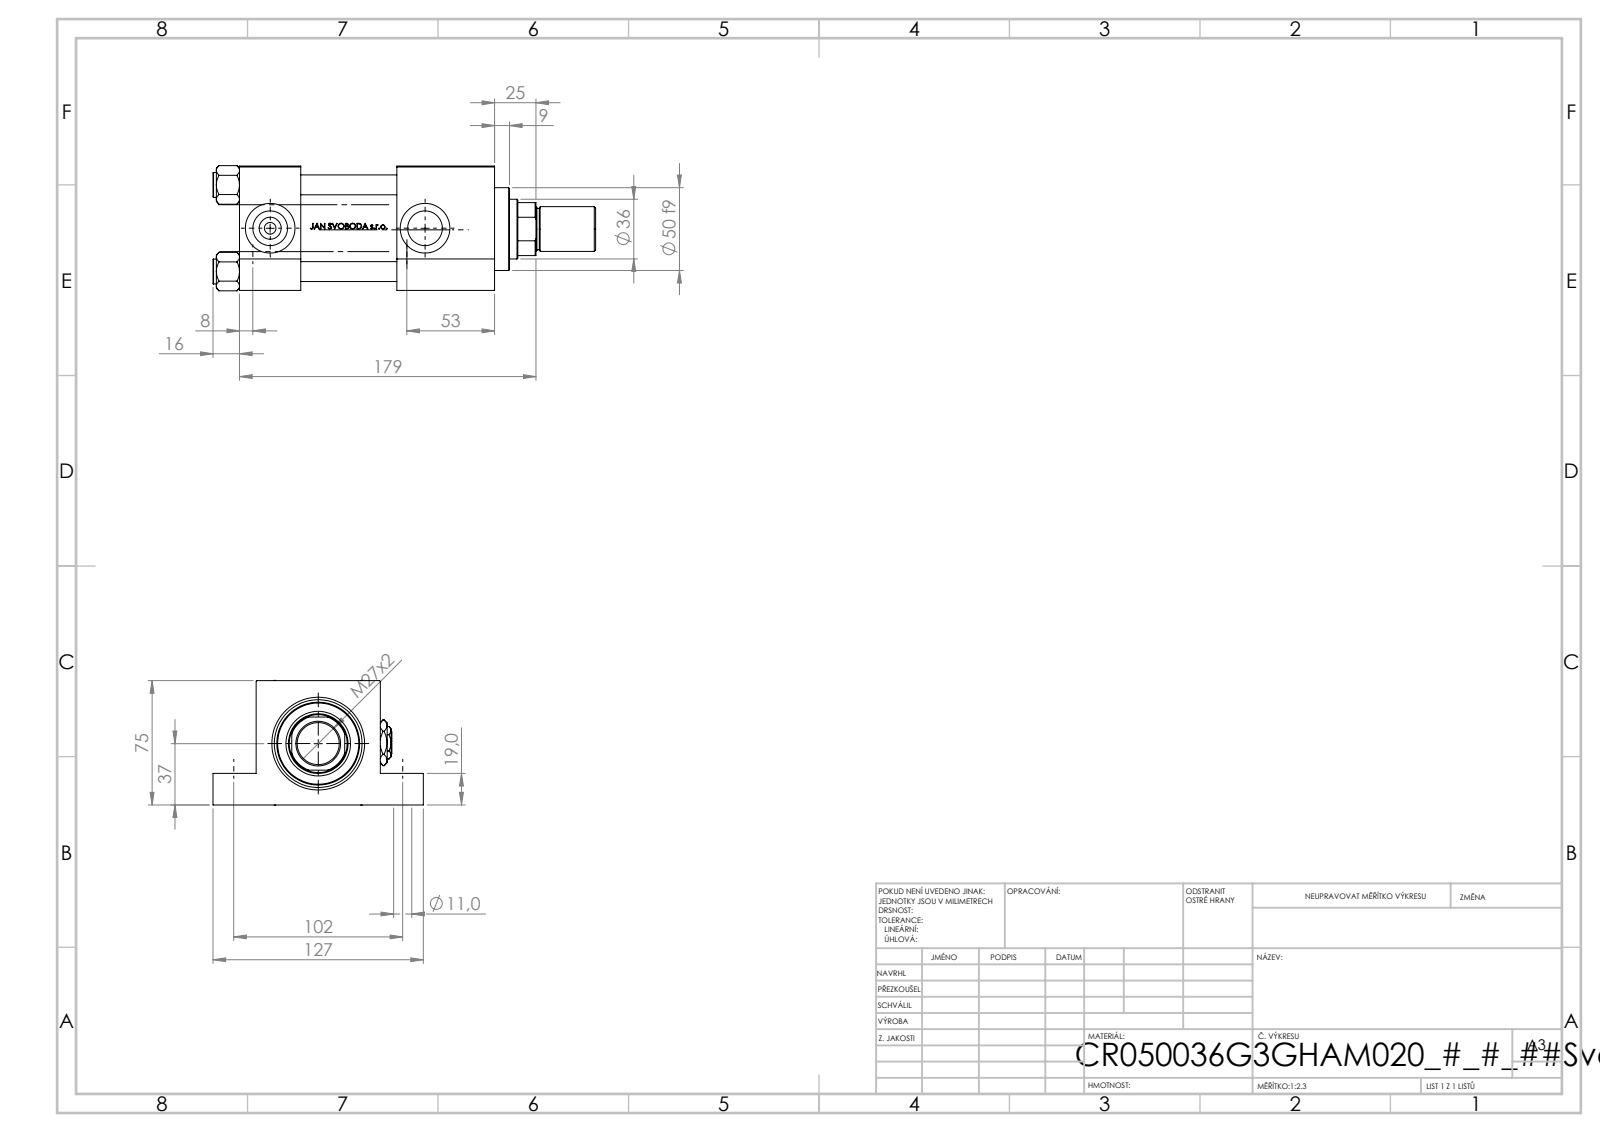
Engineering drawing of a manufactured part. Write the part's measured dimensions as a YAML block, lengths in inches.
part_name: "NUT_M5_G; V215CR_G_Body; V215CR_VCP_G; V215_VC_A (+3 more)"
step_written_by: "SolidWorks 2019 (CONFIG_CONTROL_DESIGN)"
units: inches
bodies: {solids: 14, faces: 1197, planar: 481, cylindrical: 136, other: 580}
overall_size: [9.094, 5, 2.974]
volume: 48.8
surface_area: 273.4
round_holes:
  - {diameter: 0.472, count: 4}
  - {diameter: 0.433, count: 3}
  - {diameter: 0.276, count: 2}
  - {diameter: 0.825, count: 2}
  - {diameter: 1.181, count: 2}
  - {diameter: 0.433, count: 1}
  - {diameter: 1.004, count: 1}
  - {diameter: 1.417, count: 1}
  - {diameter: 1.535, count: 1}
  - {diameter: 1.614, count: 1}
  - {diameter: 2.087, count: 1}
round_bosses_or_shafts:
  - {diameter: 0.591, count: 4}
  - {diameter: 2.205, count: 1}
  - {diameter: 1.969, count: 1}
  - {diameter: 1.063, count: 1}
  - {diameter: 0.984, count: 1}
partial_cylinders:
  - {radius: 0.689, count: 1}
face_to_face_distances: [2.953, 1.457, 0.748, 2.205, 6.063, 4.606, 2.323, 3.74, 2.283, 1.024]
hole_center_spacings: [2.059, 1.442, 1.47, 2.912, 4.016, 4.409, 5.964, 3.681]
